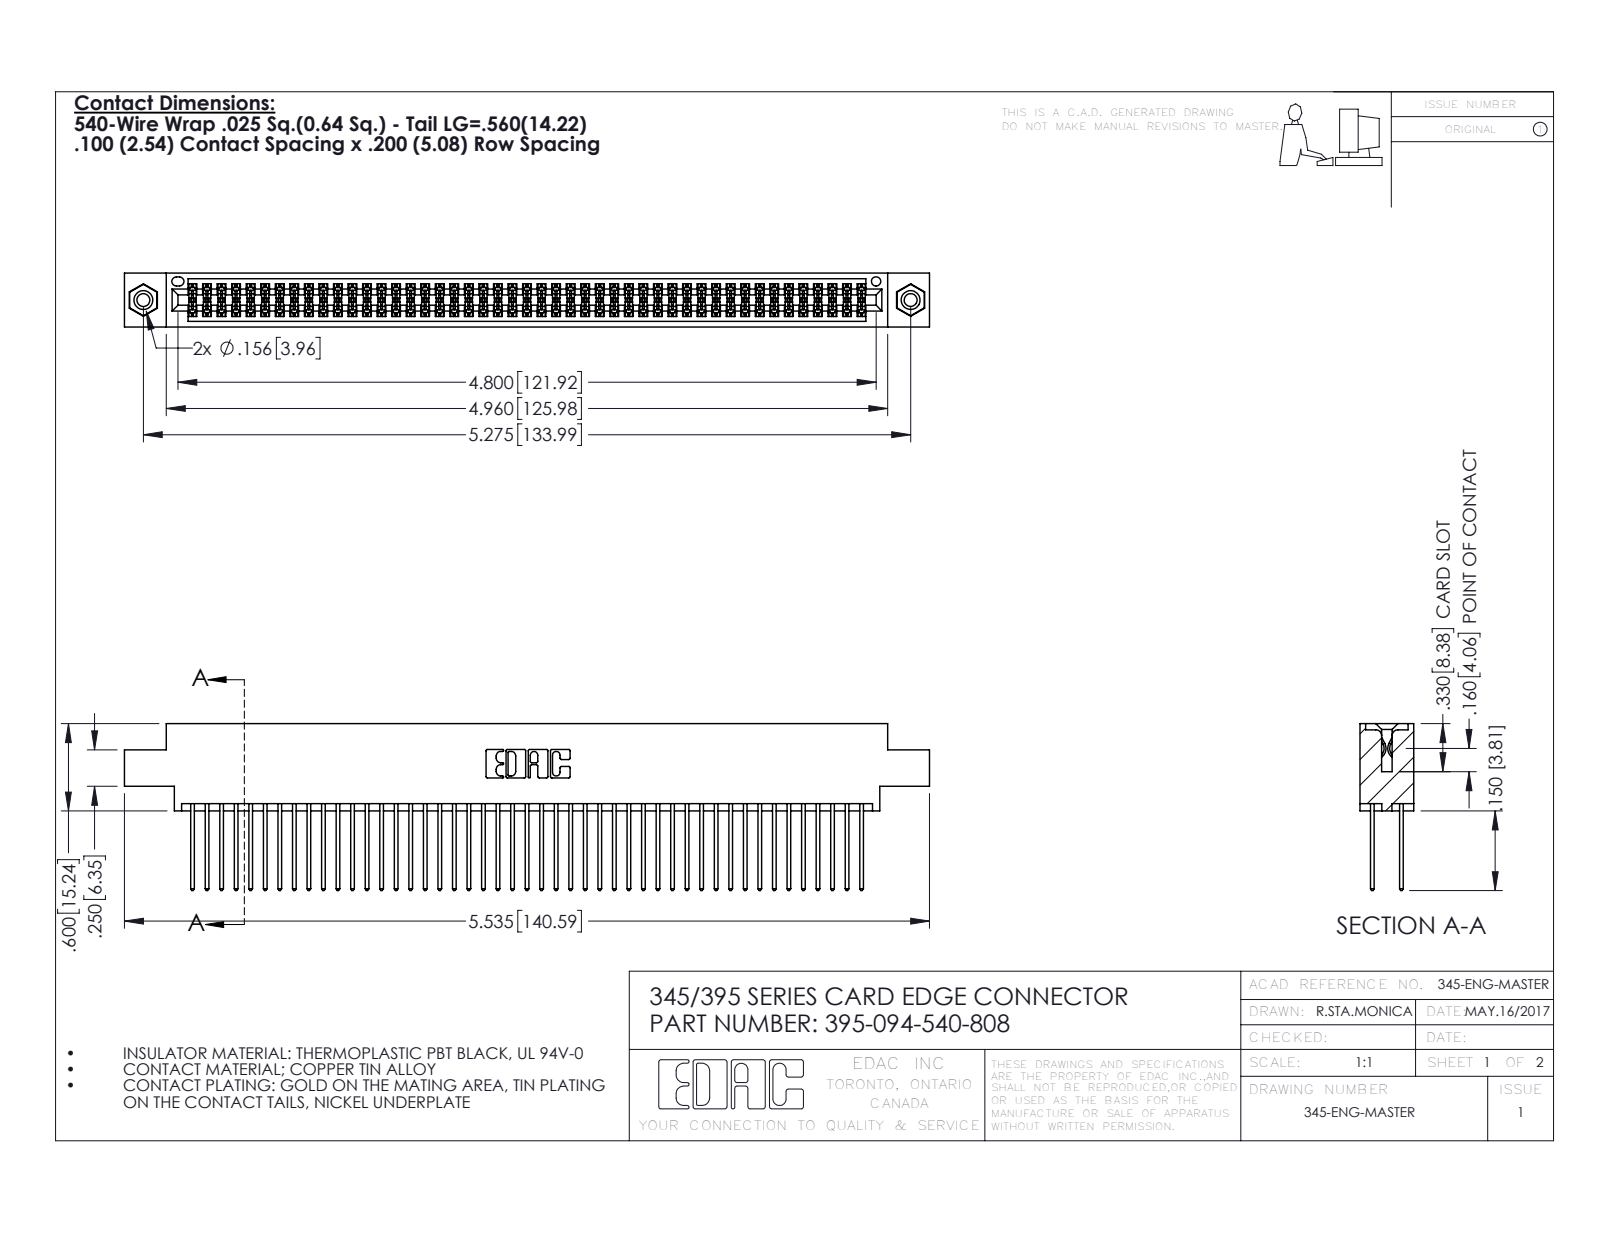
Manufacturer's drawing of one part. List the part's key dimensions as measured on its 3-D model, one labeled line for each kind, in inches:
Part name (STEP PRODUCT): 345-292-001_345-293-140; 345-250-001_345-250-003-102; 395-094-540-808; 345 Part_0.170 Offset - 0.156 Dia-TI
STEP written by: SolidWorks 2016 (CONFIG_CONTROL_DESIGN)
Units: inches
Bodies: 97 solids, 4890 faces (3218 planar, 1656 cylindrical, 16 other)
Overall size (bounding box): 5.535 × 1.147 × 0.37
Volume: 0.851 in³ · Surface area: 34.89 in²
Round holes (diameter × count): ⌀0.089 ×2, ⌀0.125 ×2, ⌀0.156 ×2, ⌀0.064 ×1
Round bosses / shafts (diameter × count): ⌀0.155 ×2
Partial cylindrical surfaces — rounded edges, fillets, slot ends (radius × count): R0.006 ×141, R0.01 ×94, R0.01 ×22, R0.007 ×6, R0.031 ×6, R0.026 ×3, R0.014 ×2, R0.019 ×2
Main face-to-face distances: 0.072, 0.298, 0.2, 0.098, 0.272, 0.025, 0.37, 0.225, 0.175, 0.149
Hole centre spacings: 0.27, 5.039, 5.275
